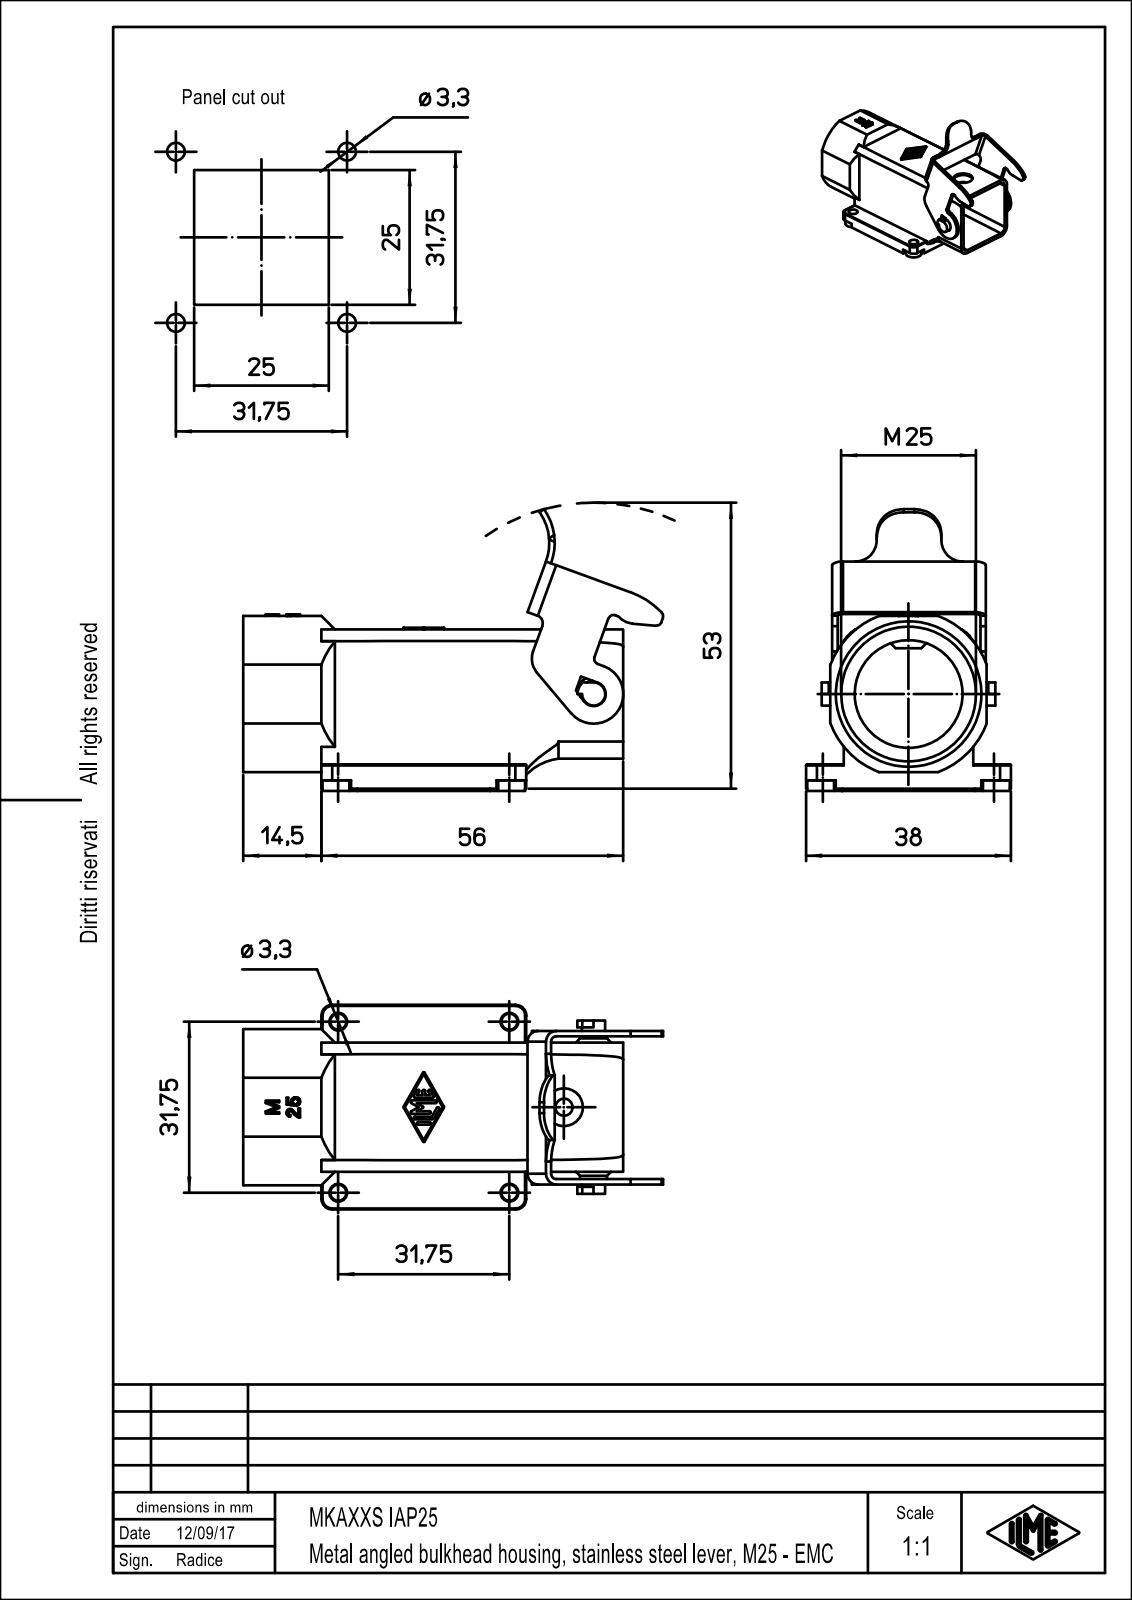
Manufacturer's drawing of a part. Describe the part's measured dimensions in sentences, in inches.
The part is named "MKAXXS_IAP25". Its 3-D file was written by "PTC Creo Elements/Direct Modeling 19.0E 27-Jun-2016 (C) Parametric Technology GmbH (AUTOMOTIVE_DESIGN)". It is 1 solid with 431 faces: 278 planar, 132 cylindrical and 21 other. Overall it measures 3.067 by 2.059 by 1.496 inches. Its volume is 0.957 cubic inches and its surface area 27.81 square inches. Round holes: 4 of diameter 0.118, 4 of diameter 0.13, 1 of diameter 0.126, 1 of diameter 0.276, 1 of diameter 0.787, 1 of diameter 0.984. Round bosses or shafts: 1 of diameter 0.197, 1 of diameter 0.169. Partial cylindrical surfaces (rounded edges, fillets, slot ends): 18 of radius 0.079, 15 of radius 0.01, 12 of radius 0.008, 10 of radius 0.126, 6 of radius 0.039, 4 of radius 0.114, 4 of radius 0.157, 3 of radius 0.005. The main face-to-face distances are 0.047, 0.898, 0.945, 0.85, 1.043, 0.039, 0.093, 0.99, 1.083, 1.181. The hole center spacings are 1.25, 1.763, 1.768, 0.741, 0.742.
